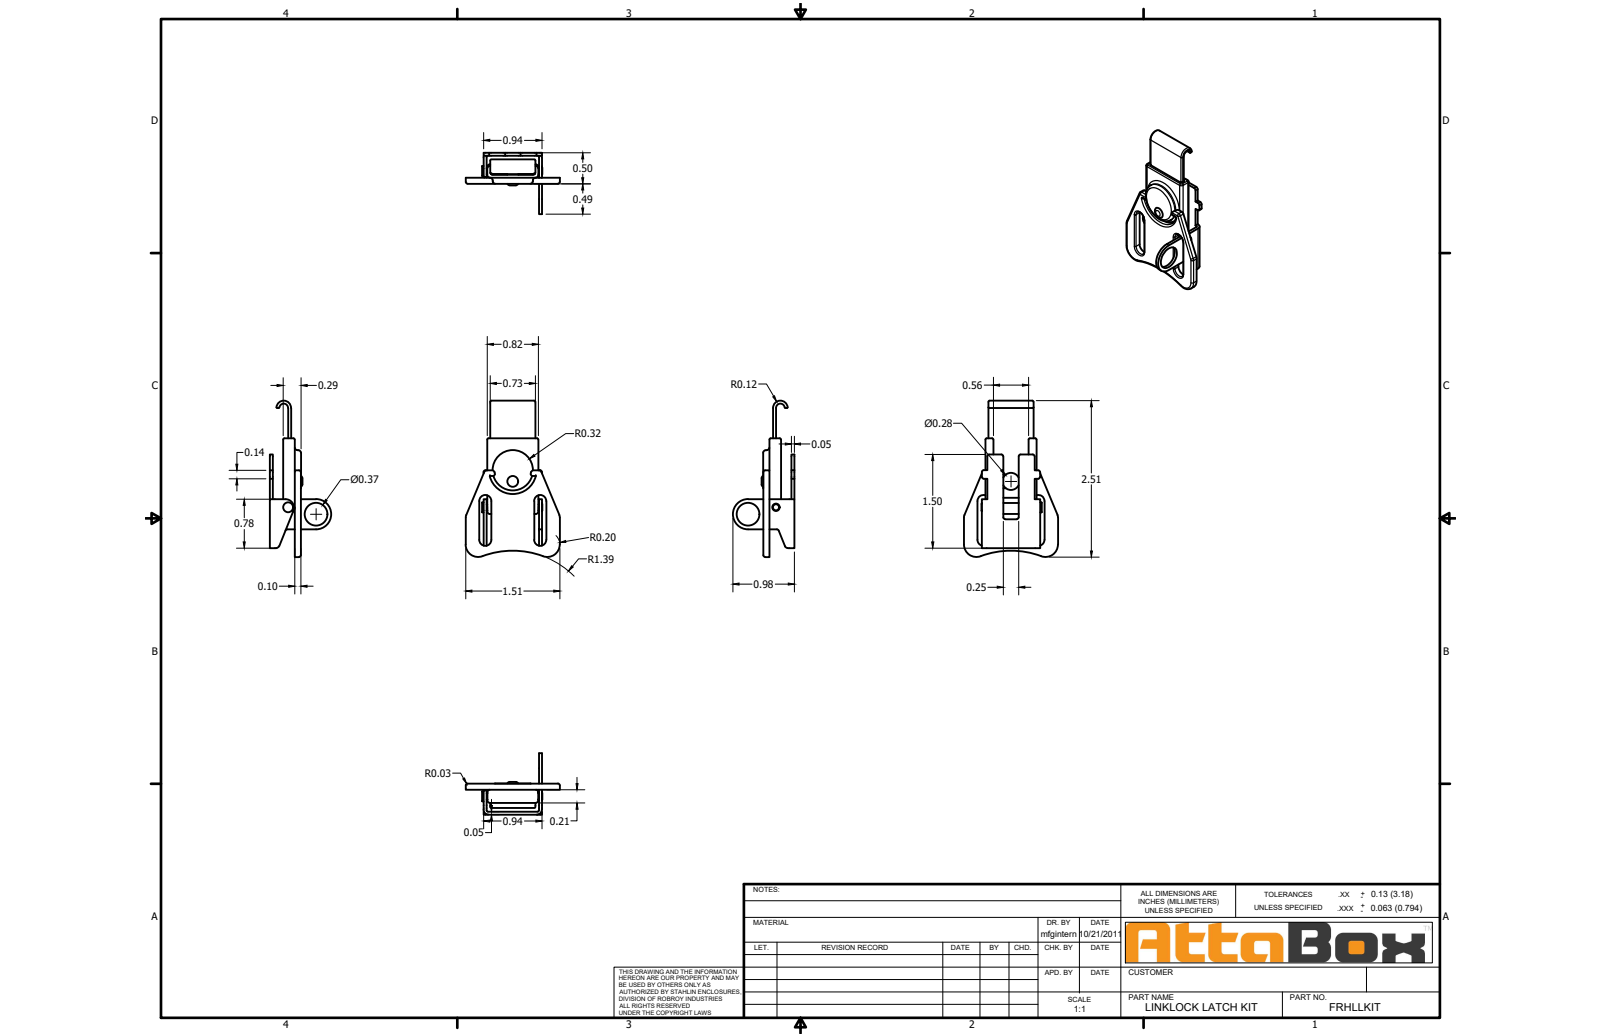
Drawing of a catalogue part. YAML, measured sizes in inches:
part_name: "FRHLLKIT"
step_written_by: "SolidWorks 2018 (AUTOMOTIVE_DESIGN)"
units: inches
bodies: {solids: 6, faces: 181, planar: 81, cylindrical: 72, other: 28}
overall_size: [2.53, 1.7, 1]
volume: 0.514
surface_area: 16.37
round_holes:
  - {diameter: 0.05, count: 1}
  - {diameter: 0.098, count: 1}
  - {diameter: 0.12, count: 1}
  - {diameter: 0.363, count: 1}
round_bosses_or_shafts:
  - {diameter: 0.6, count: 1}
  - {diameter: 0.2, count: 1}
  - {diameter: 0.135, count: 1}
  - {diameter: 0.05, count: 1}
partial_cylinders:
  - {radius: 0.039, count: 14}
  - {radius: 0.01, count: 10}
  - {radius: 0.008, count: 8}
  - {radius: 0.1, count: 6}
  - {radius: 0.125, count: 6}
  - {radius: 0.098, count: 4}
  - {radius: 0.094, count: 3}
  - {radius: 0.031, count: 2}
face_to_face_distances: [0.063, 0.094, 0.125, 0.05, 0.062, 0.063, 0.125, 0.188, 0.048, 0.892]
hole_center_spacings: [0.429, 0.754, 0.793]
